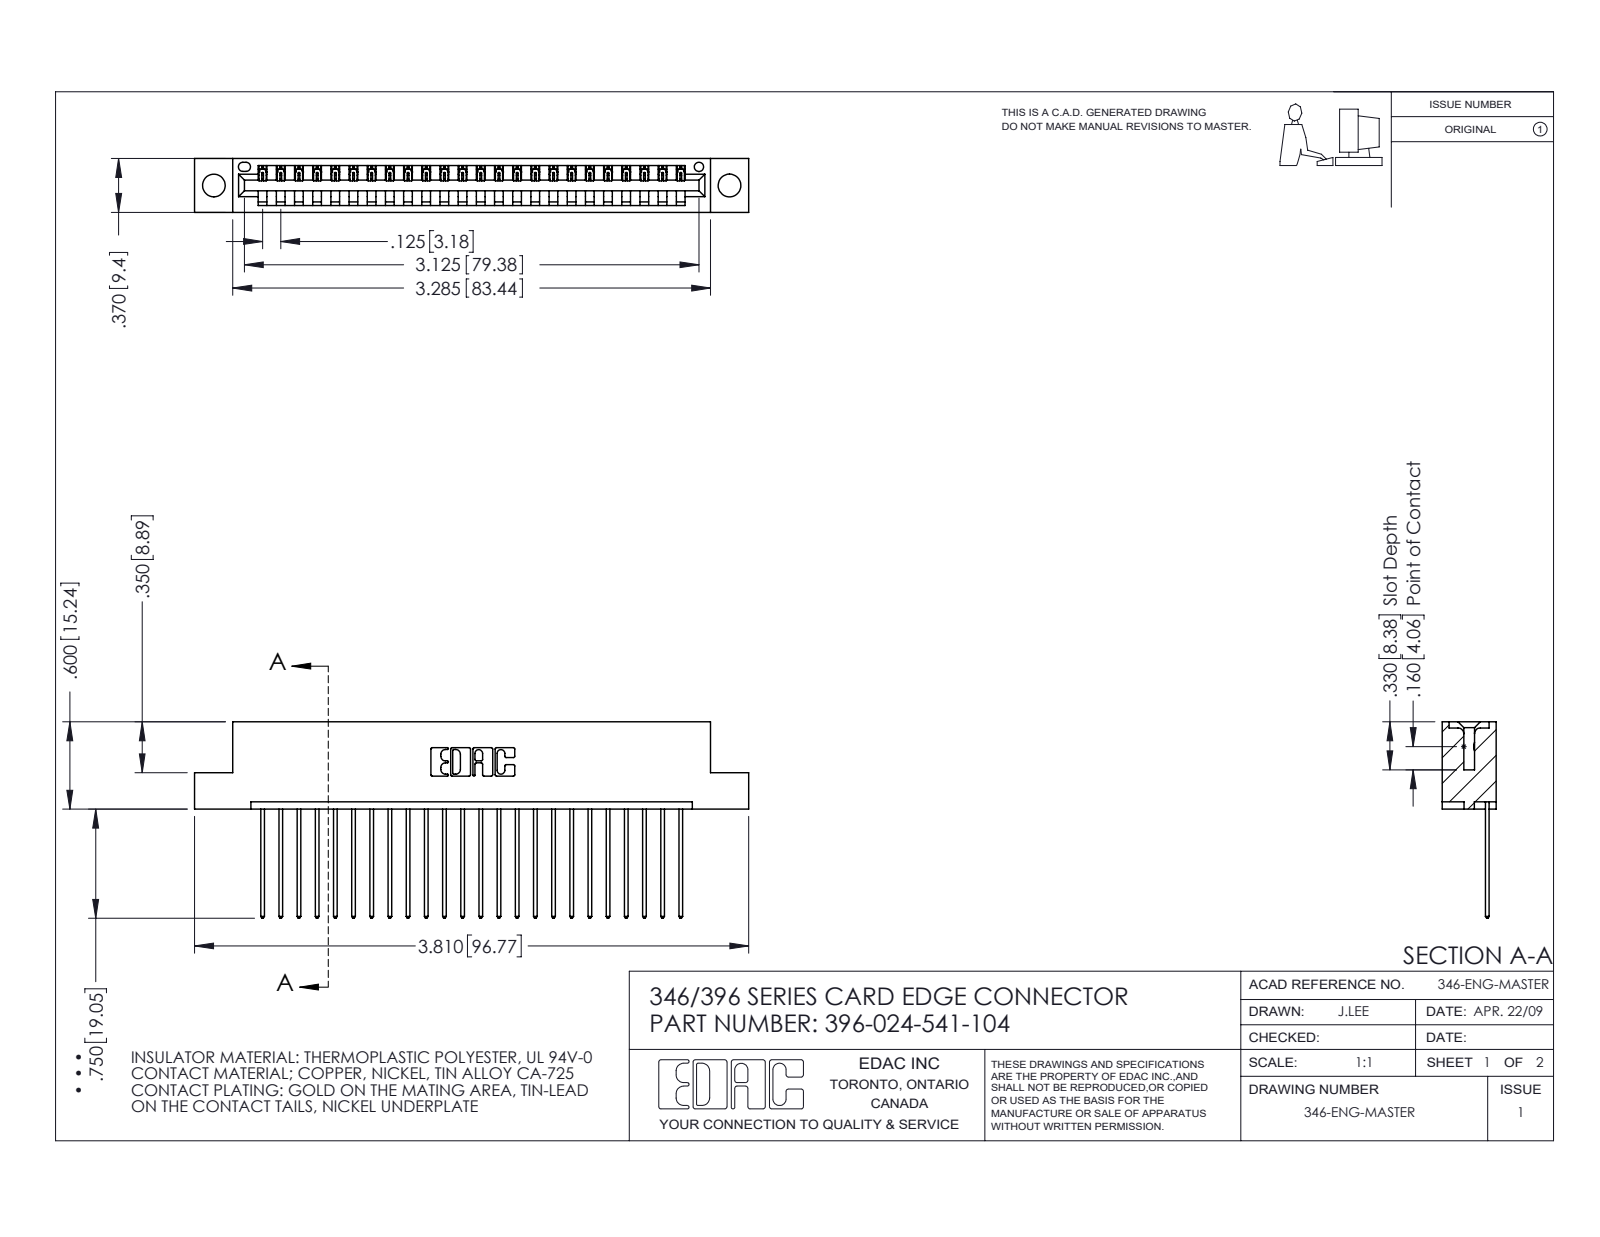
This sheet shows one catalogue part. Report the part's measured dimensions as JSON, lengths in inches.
{"part_name": "396-024-541-104; 345-292-001_345-293-141; 346 Part_Flush Mounting Lugs - 0.156 Dia-TH", "step_written_by": "SolidWorks 2016 (CONFIG_CONTROL_DESIGN)", "units": "inches", "bodies": {"solids": 25, "faces": 1514, "planar": 1036, "cylindrical": 478, "other": 0}, "overall_size": [3.81, 1.35, 0.37], "volume_in3": 0.557, "surface_area_in2": 17.82, "round_holes": [[0.156, 2], [0.064, 1]], "partial_cylinders_radius": [[0.006, 48], [0.01, 48], [0.01, 22], [0.007, 6], [0.031, 6], [0.026, 3], [0.031, 2], [0.04, 2]], "face_to_face_distances": [0.048, 0.322, 0.25, 0.37, 0.072, 0.298, 0.025, 0.148, 0.222, 0.1], "hole_center_spacings": [0.246, 3.337, 3.545]}
